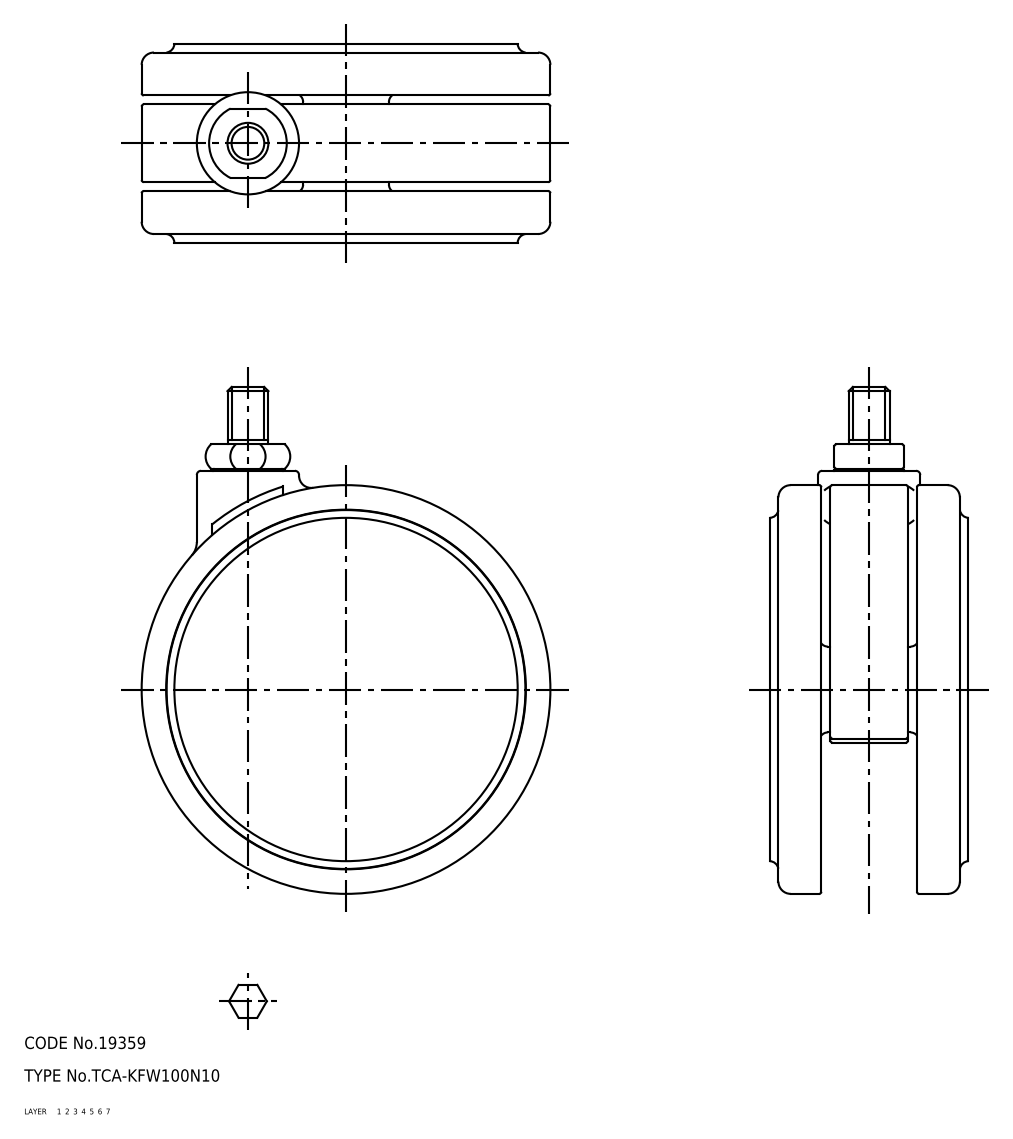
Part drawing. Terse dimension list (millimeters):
name: caster; TCA-KFW100N10
written by: SolidWorks 2015 (AUTOMOTIVE_DESIGN)
unit: mm
bodies: 1 solid, 999 faces (379 planar, 396 cylindrical, 224 other)
size: 124 × 100 × 48.6
volume: 176 543 mm³; area: 88 973 mm²
holes: 1× ⌀7.98, 1× ⌀8.07, 1× ⌀9.3, 1× ⌀10.7, 1× ⌀12.3, 1× ⌀13, 1× ⌀24, 1× ⌀81, 1× ⌀88
bosses: 1× ⌀100, 1× ⌀87.8, 1× ⌀25, 1× ⌀22, 1× ⌀17, 1× ⌀10.5, 1× ⌀10, 1× ⌀6.5
rounds: 30× R1, 19× R0.5, 16× R0.2, 10× R2, 9× R1.5, 6× R3, 1× R4, 1× R8
face distances: 1.8, 45, 46.8, 3.6, 43.2, 7.6, 12.6, 9, 10.8, 36
